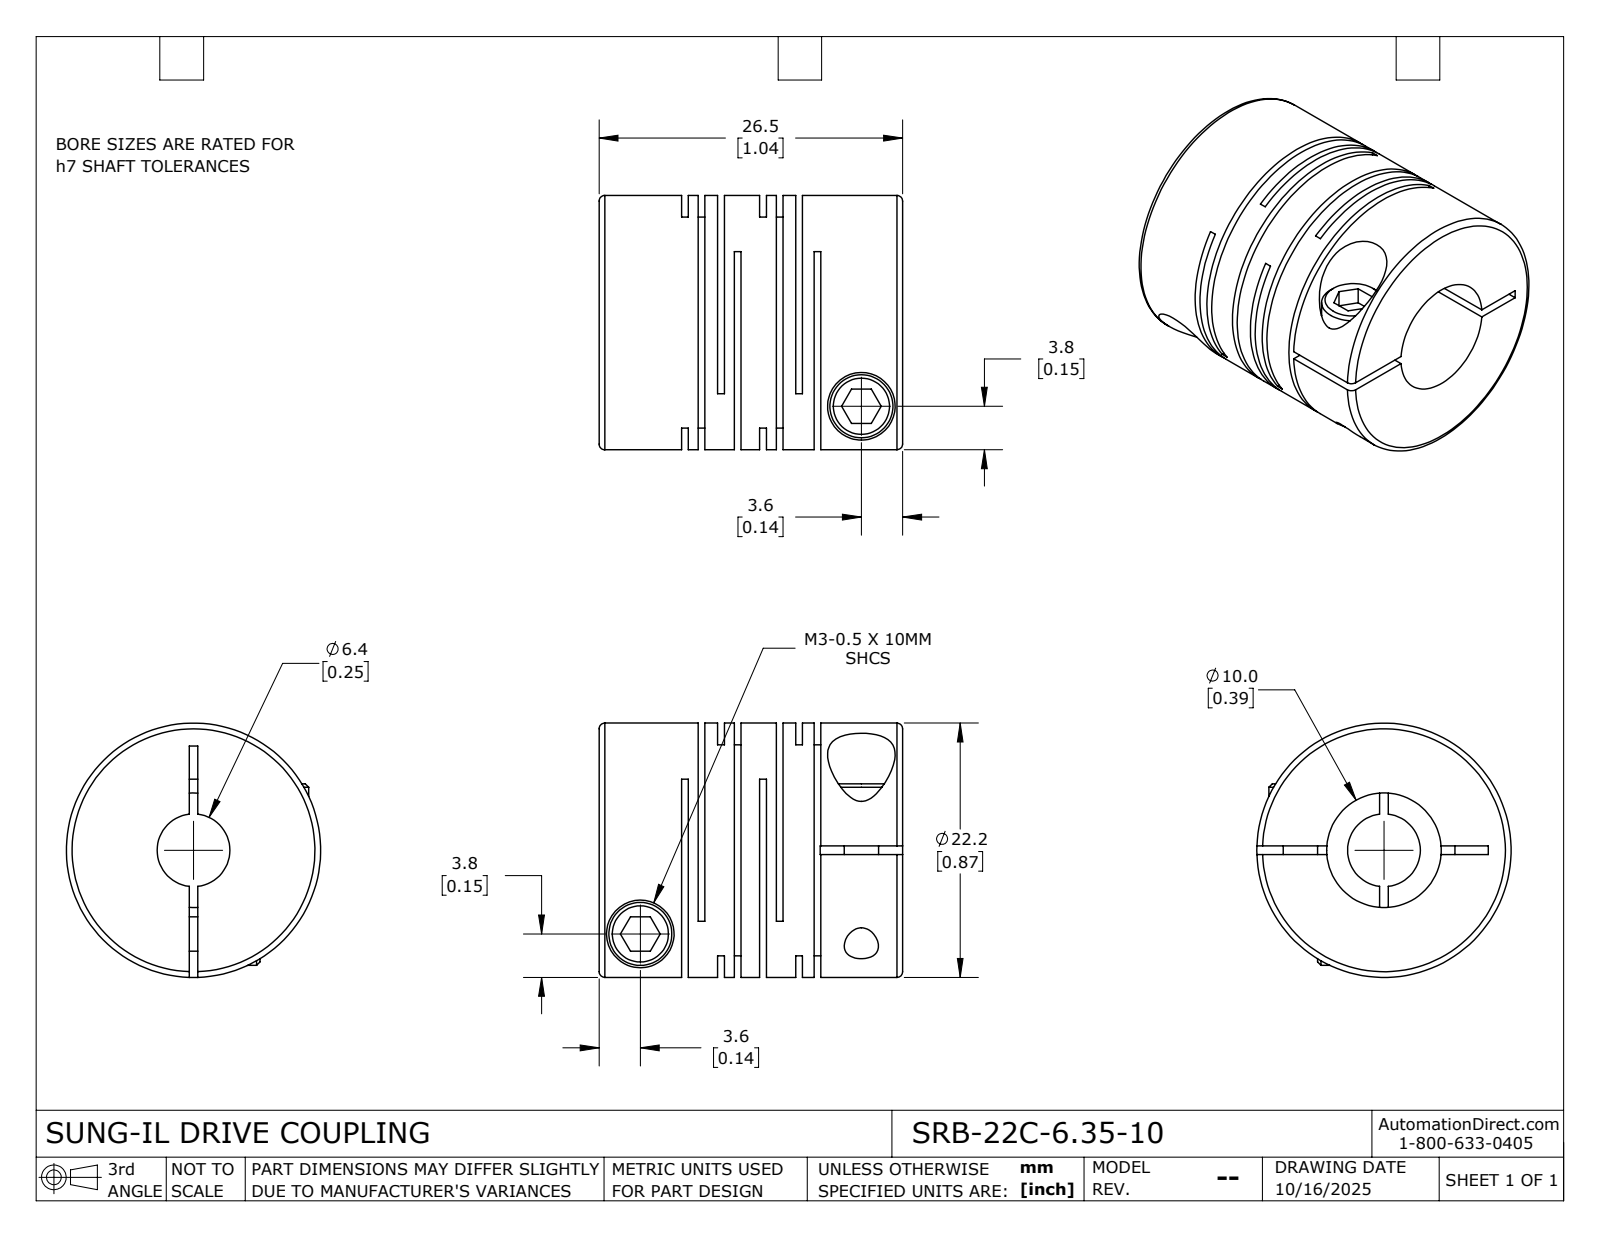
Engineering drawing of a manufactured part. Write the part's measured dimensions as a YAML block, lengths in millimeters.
part_name: "SRB-22C-6.35-10"
step_written_by: "SolidWorks 2024 (CONFIG_CONTROL_DESIGN)"
units: millimeters
bodies: {solids: 1, faces: 115, planar: 60, cylindrical: 42, other: 13}
overall_size: [26.5, 22.2, 22.2]
volume: 7039
surface_area: 7476
round_holes:
  - {diameter: 3, count: 2}
  - {diameter: 5.9, count: 2}
  - {diameter: 6.35, count: 1}
  - {diameter: 10, count: 1}
round_bosses_or_shafts:
  - {diameter: 5.5, count: 2}
  - {diameter: 22.2, count: 1}
face_to_face_distances: [0.59, 3.15, 6.82, 1.45, 5.37, 3.67, 1.7, 2.04, 3.74, 7.41]
